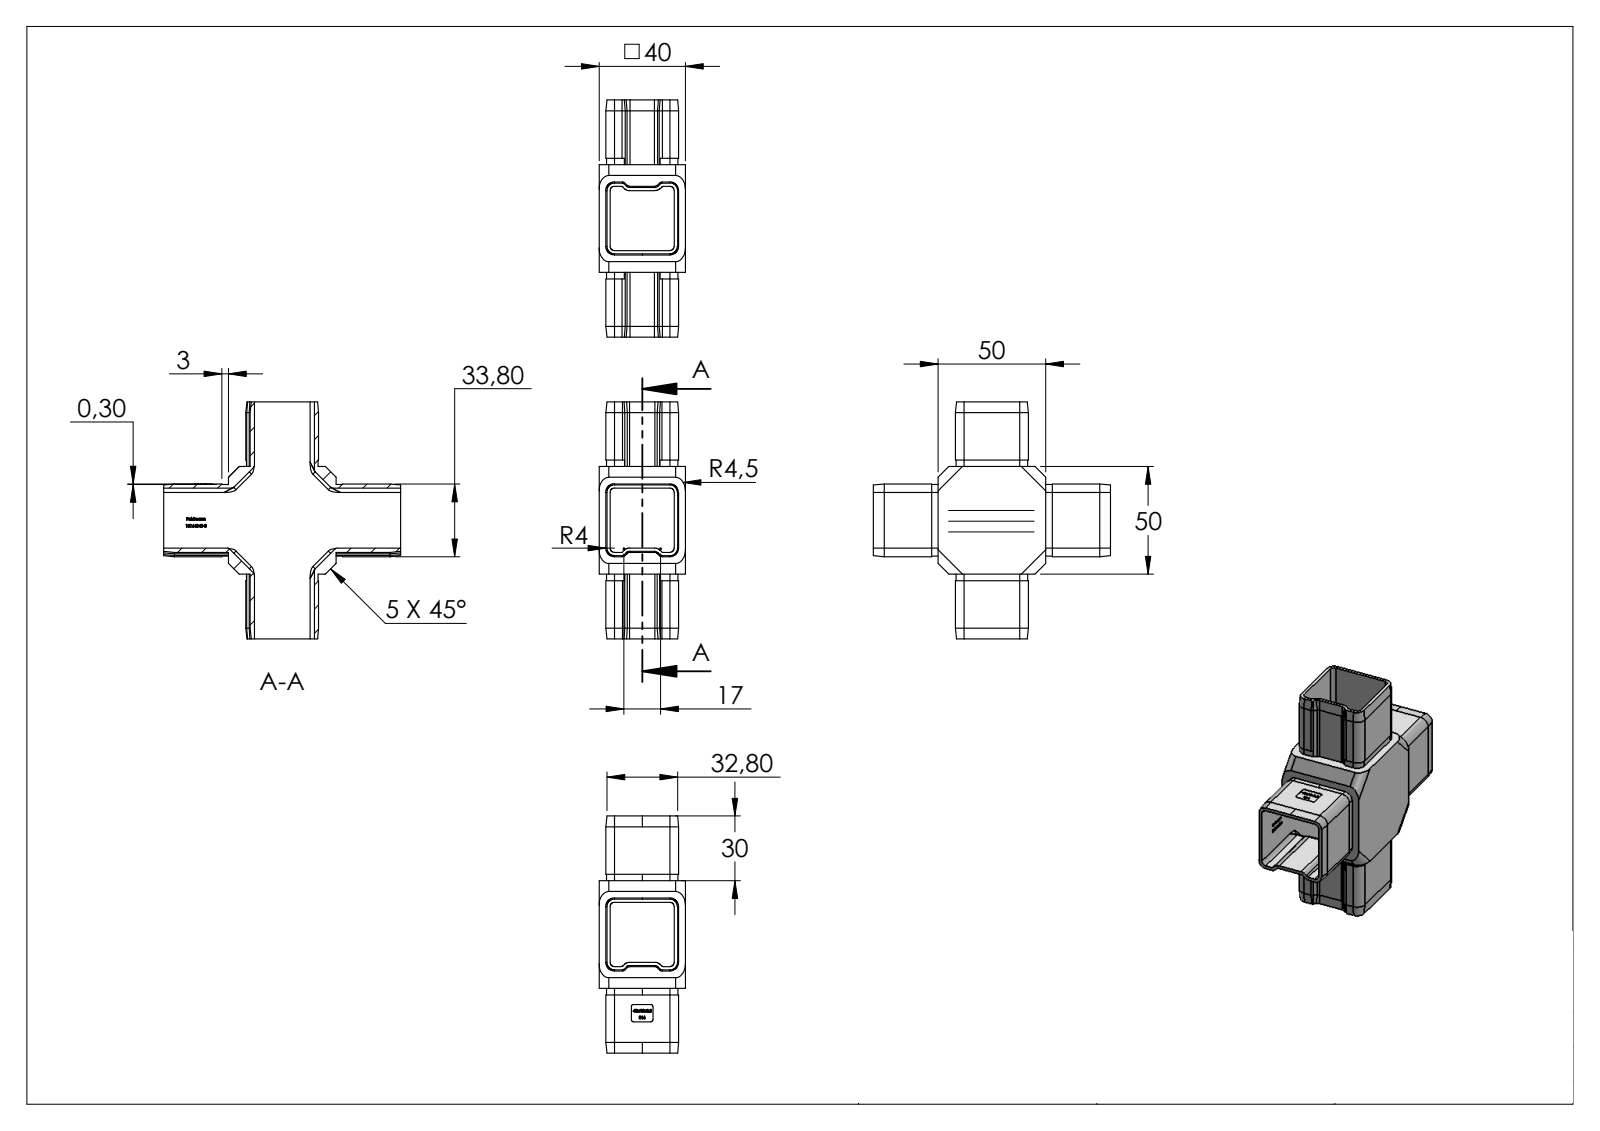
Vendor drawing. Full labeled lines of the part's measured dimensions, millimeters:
Part name (STEP PRODUCT): 10164040-3
STEP written by: SolidWorks 2015 (CONFIG_CONTROL_DESIGN)
Units: millimetres
Bodies: 1 solid, 734 faces (390 planar, 120 cylindrical, 224 other)
Overall size (bounding box): 110 × 110 × 40
Volume: 60 324 mm³ · Surface area: 44 682 mm²
Partial cylindrical surfaces — rounded edges, fillets, slot ends (radius × count): R1.5 ×34, R2 ×12, R4 ×10, R3.7 ×8, R4.5 ×8, R1 ×4, R3.5 ×2
Main face-to-face distances: 2, 29.8, 31.8, 5.1, 3.1, 34.9, 36.9, 33.8, 40, 10.1
